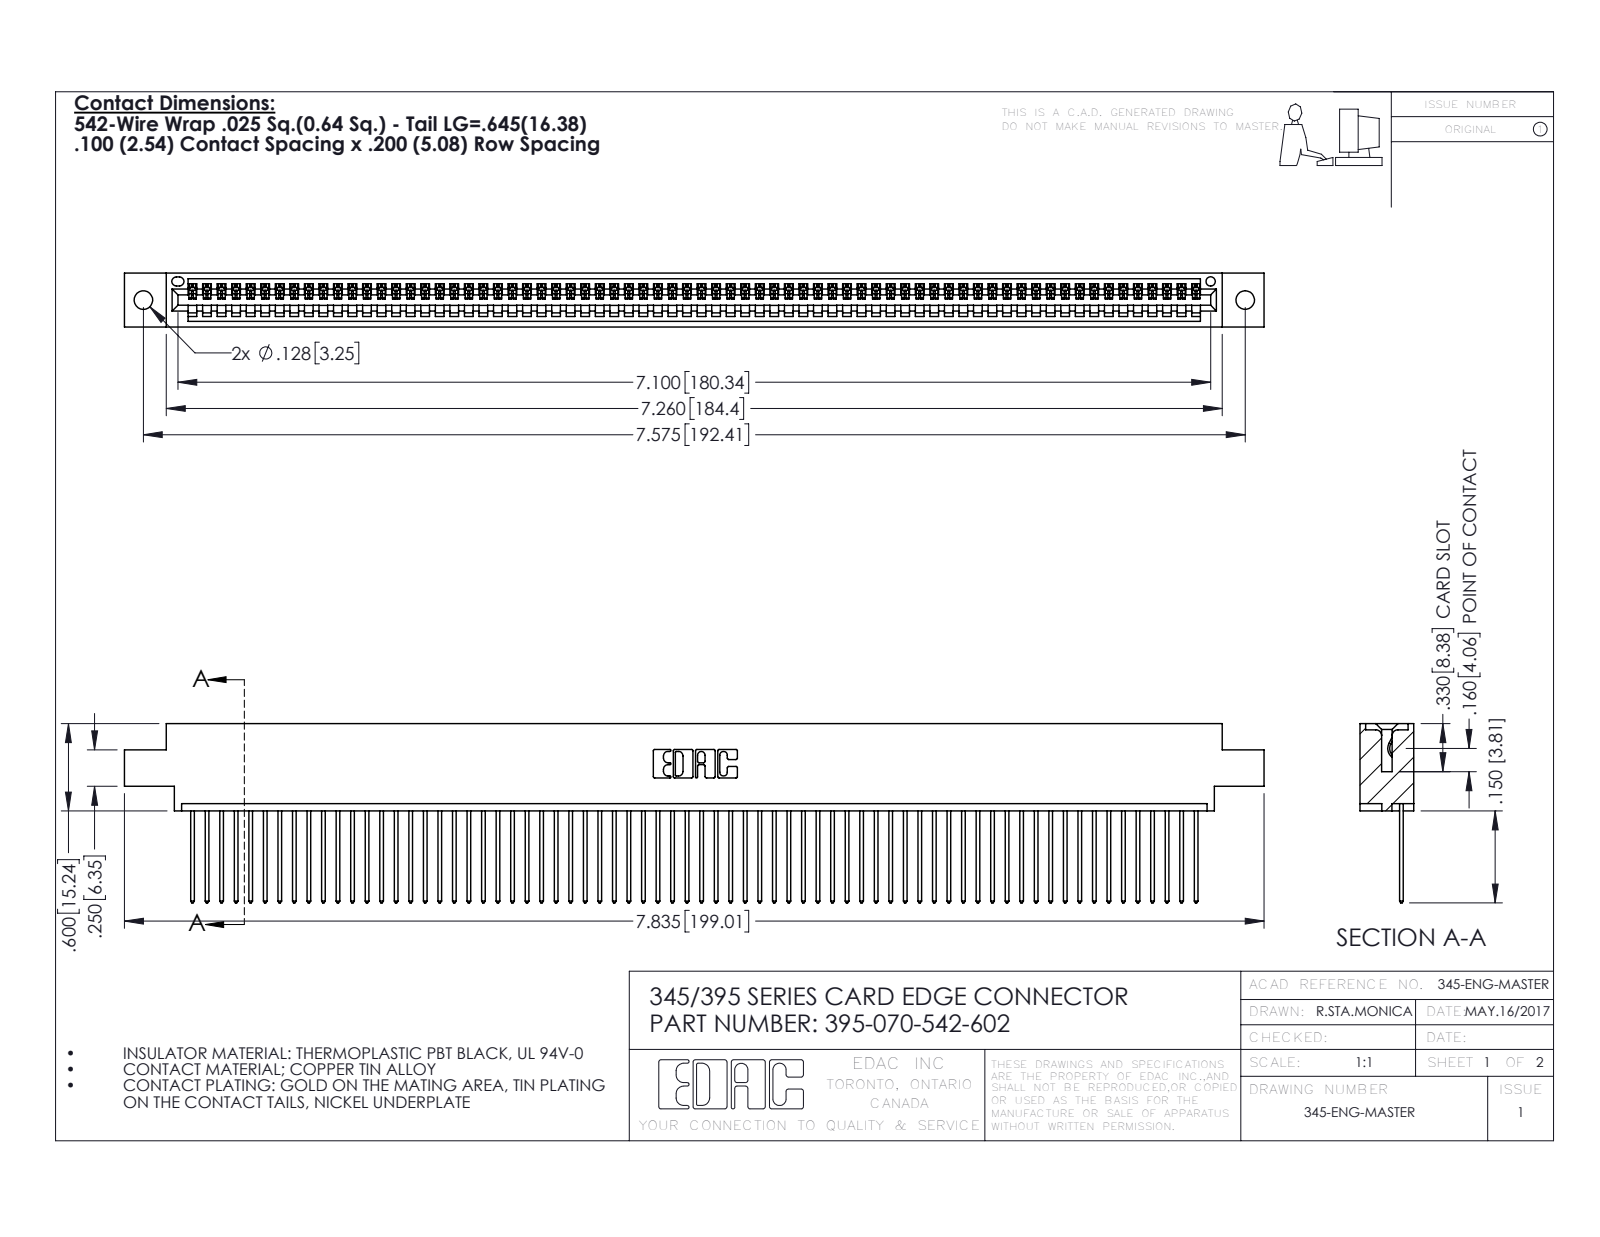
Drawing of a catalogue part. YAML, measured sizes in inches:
part_name: "395-070-542-602; 345 Part_0.170 Offset - 0.128 Dia; 345-292-001_345-293-142"
step_written_by: "SolidWorks 2016 (CONFIG_CONTROL_DESIGN)"
units: inches
bodies: {solids: 71, faces: 4190, planar: 2884, cylindrical: 1306, other: 0}
overall_size: [7.835, 1.232, 0.37]
volume: 1.168
surface_area: 41.31
round_holes:
  - {diameter: 0.128, count: 2}
  - {diameter: 0.064, count: 1}
partial_cylinders:
  - {radius: 0.006, count: 140}
  - {radius: 0.01, count: 140}
  - {radius: 0.01, count: 22}
  - {radius: 0.007, count: 6}
  - {radius: 0.031, count: 6}
  - {radius: 0.026, count: 3}
  - {radius: 0.031, count: 2}
  - {radius: 0.04, count: 2}
face_to_face_distances: [0.072, 0.298, 0.37, 0.098, 0.272, 0.025, 0.2, 0.225, 0.175, 0.149]
hole_center_spacings: [0.27, 7.339, 7.575]
